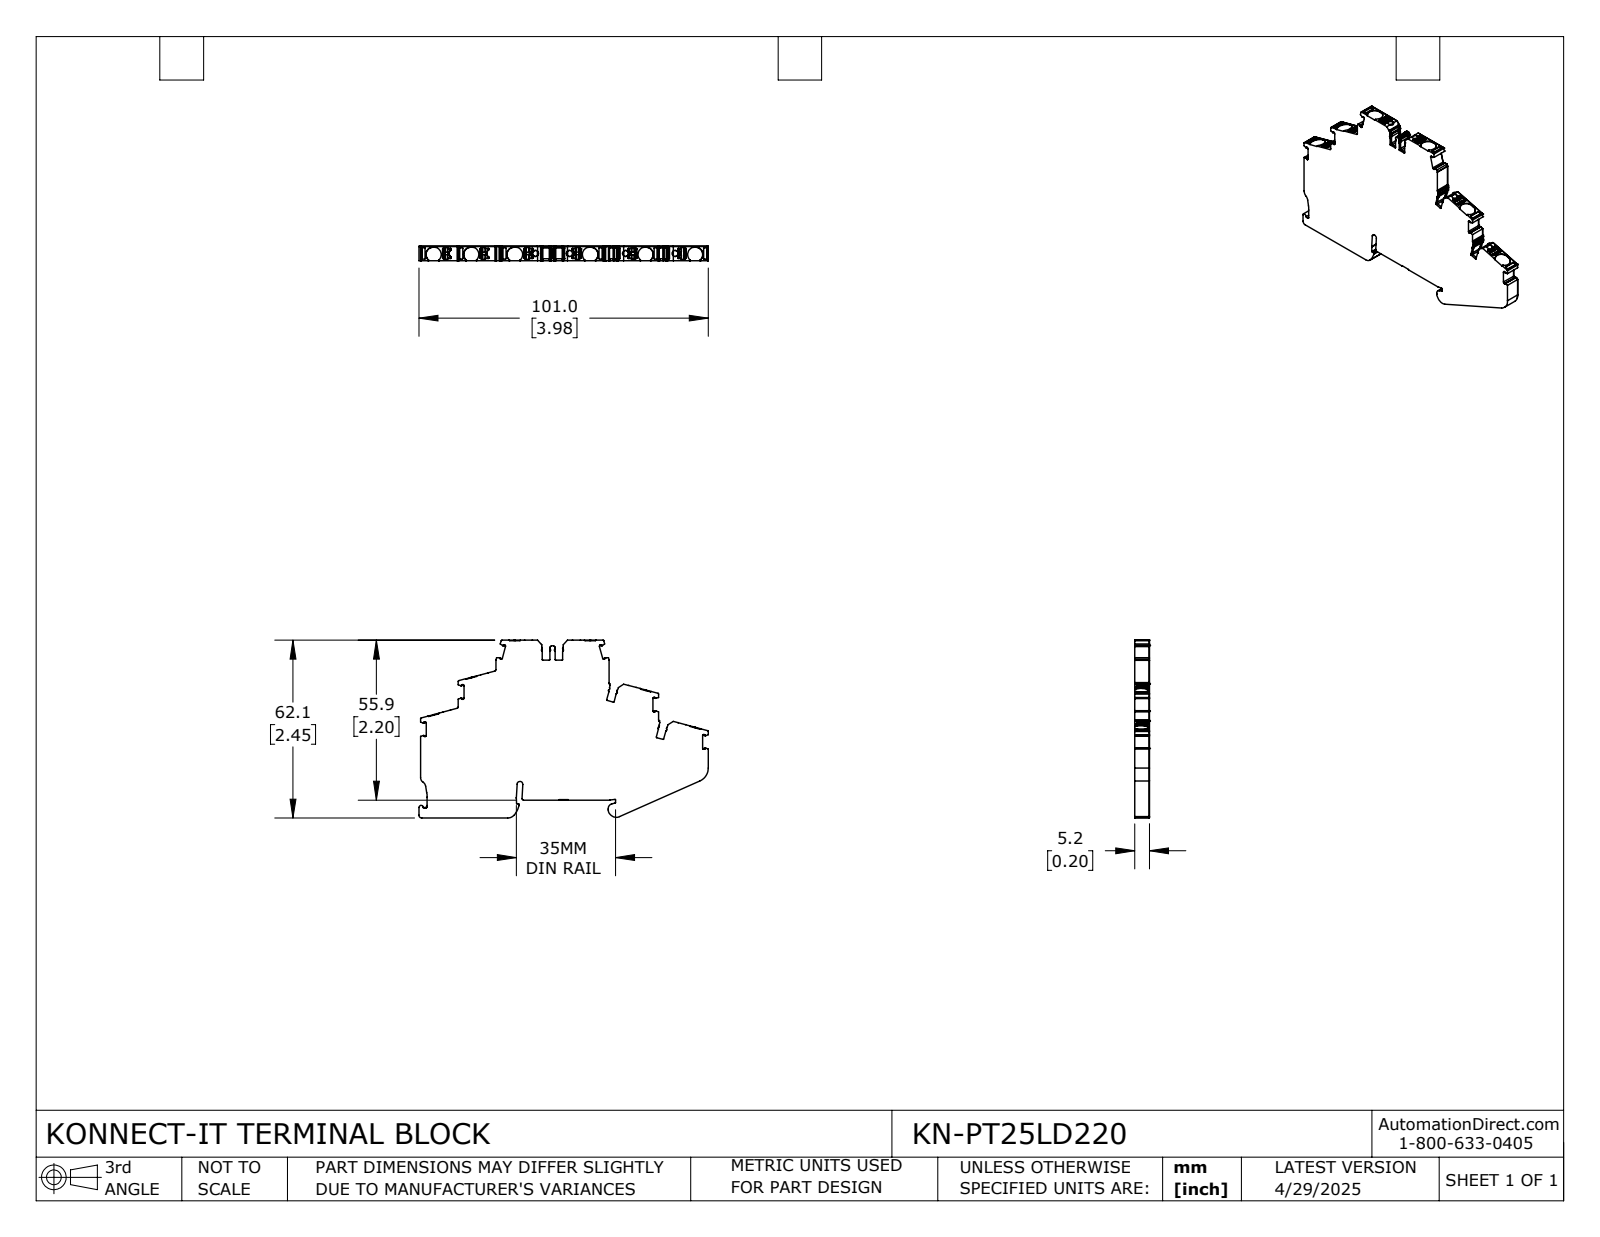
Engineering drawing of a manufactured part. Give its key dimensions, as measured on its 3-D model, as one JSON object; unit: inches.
{"part_name": "KN-PT25LD220", "step_written_by": "SolidWorks 2024 (CONFIG_CONTROL_DESIGN)", "units": "inches", "bodies": {"solids": 1, "faces": 1212, "planar": 579, "cylindrical": 528, "other": 105}, "overall_size": [3.977, 2.445, 0.203], "volume_in3": 1.354, "surface_area_in2": 16.76, "round_holes": [[0.083, 4]], "partial_cylinders_radius": [[0.008, 128], [0.004, 49], [0.012, 47], [0.02, 26], [0.006, 24], [0.016, 17], [0.024, 14], [0.006, 12]], "face_to_face_distances": [0.203, 0.246, 0.079, 2.191, 2.437, 0.319, 0.682, 0.519, 2.445, 2.199], "hole_center_spacings": [0.466, 0.792]}
